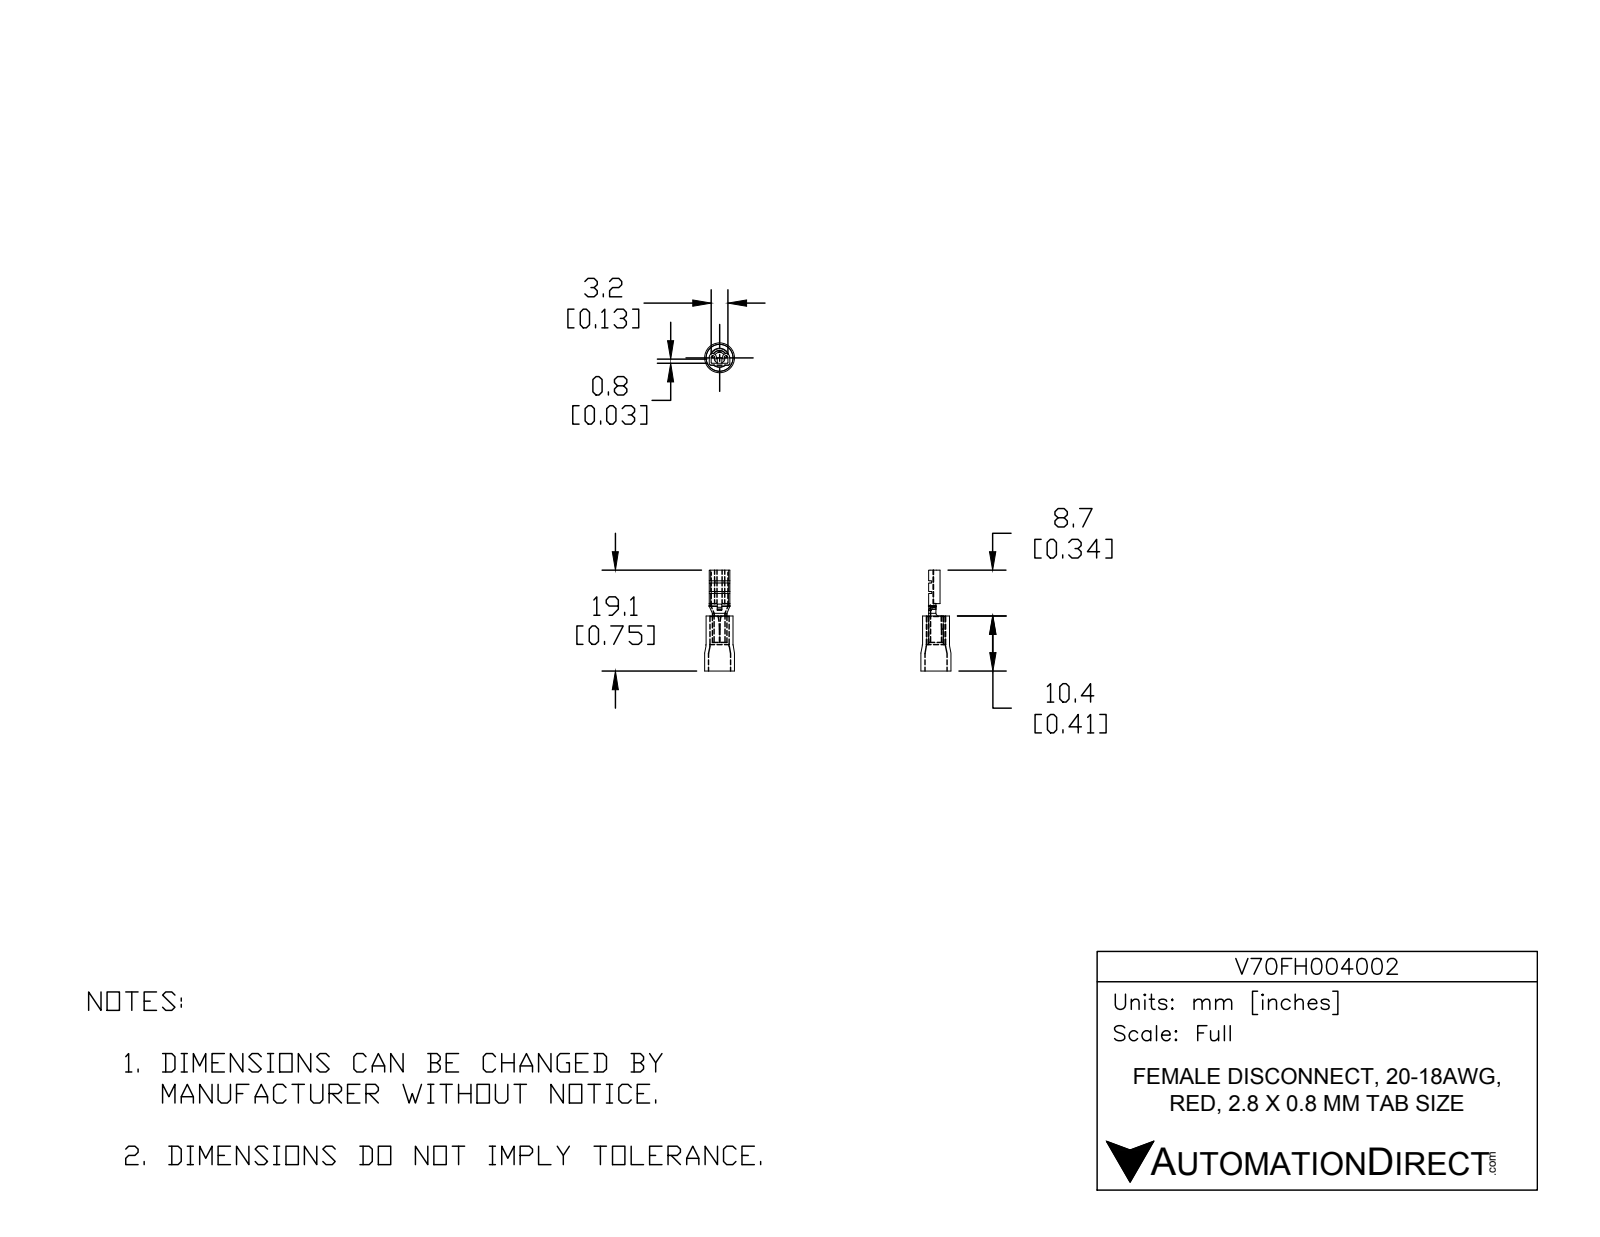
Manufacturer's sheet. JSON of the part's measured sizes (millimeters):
{"part_name": "V70FH004002", "step_written_by": "SolidWorks 2017 (AUTOMOTIVE_DESIGN)", "units": "millimeters", "bodies": {"solids": 3, "faces": 121, "planar": 49, "cylindrical": 38, "other": 34}, "overall_size": [18.82, 5.68, 5.68], "volume_mm3": 182, "surface_area_mm2": 754, "round_holes": [[2.05, 1], [2.78, 1], [3.6, 1], [4.18, 1]], "round_bosses_or_shafts": [[5.68, 1], [5.1, 1], [3.48, 1], [2.75, 1]], "partial_cylinders_radius": [[0.12, 2], [0.25, 2], [0.38, 2], [0.73, 2], [17.33, 2], [0.39, 1], [0.5, 1], [0.74, 1]], "face_to_face_distances": [0.35, 0.36, 3.54, 10.42, 3.9, 2, 3.18, 18.82, 8.4, 10.06]}
